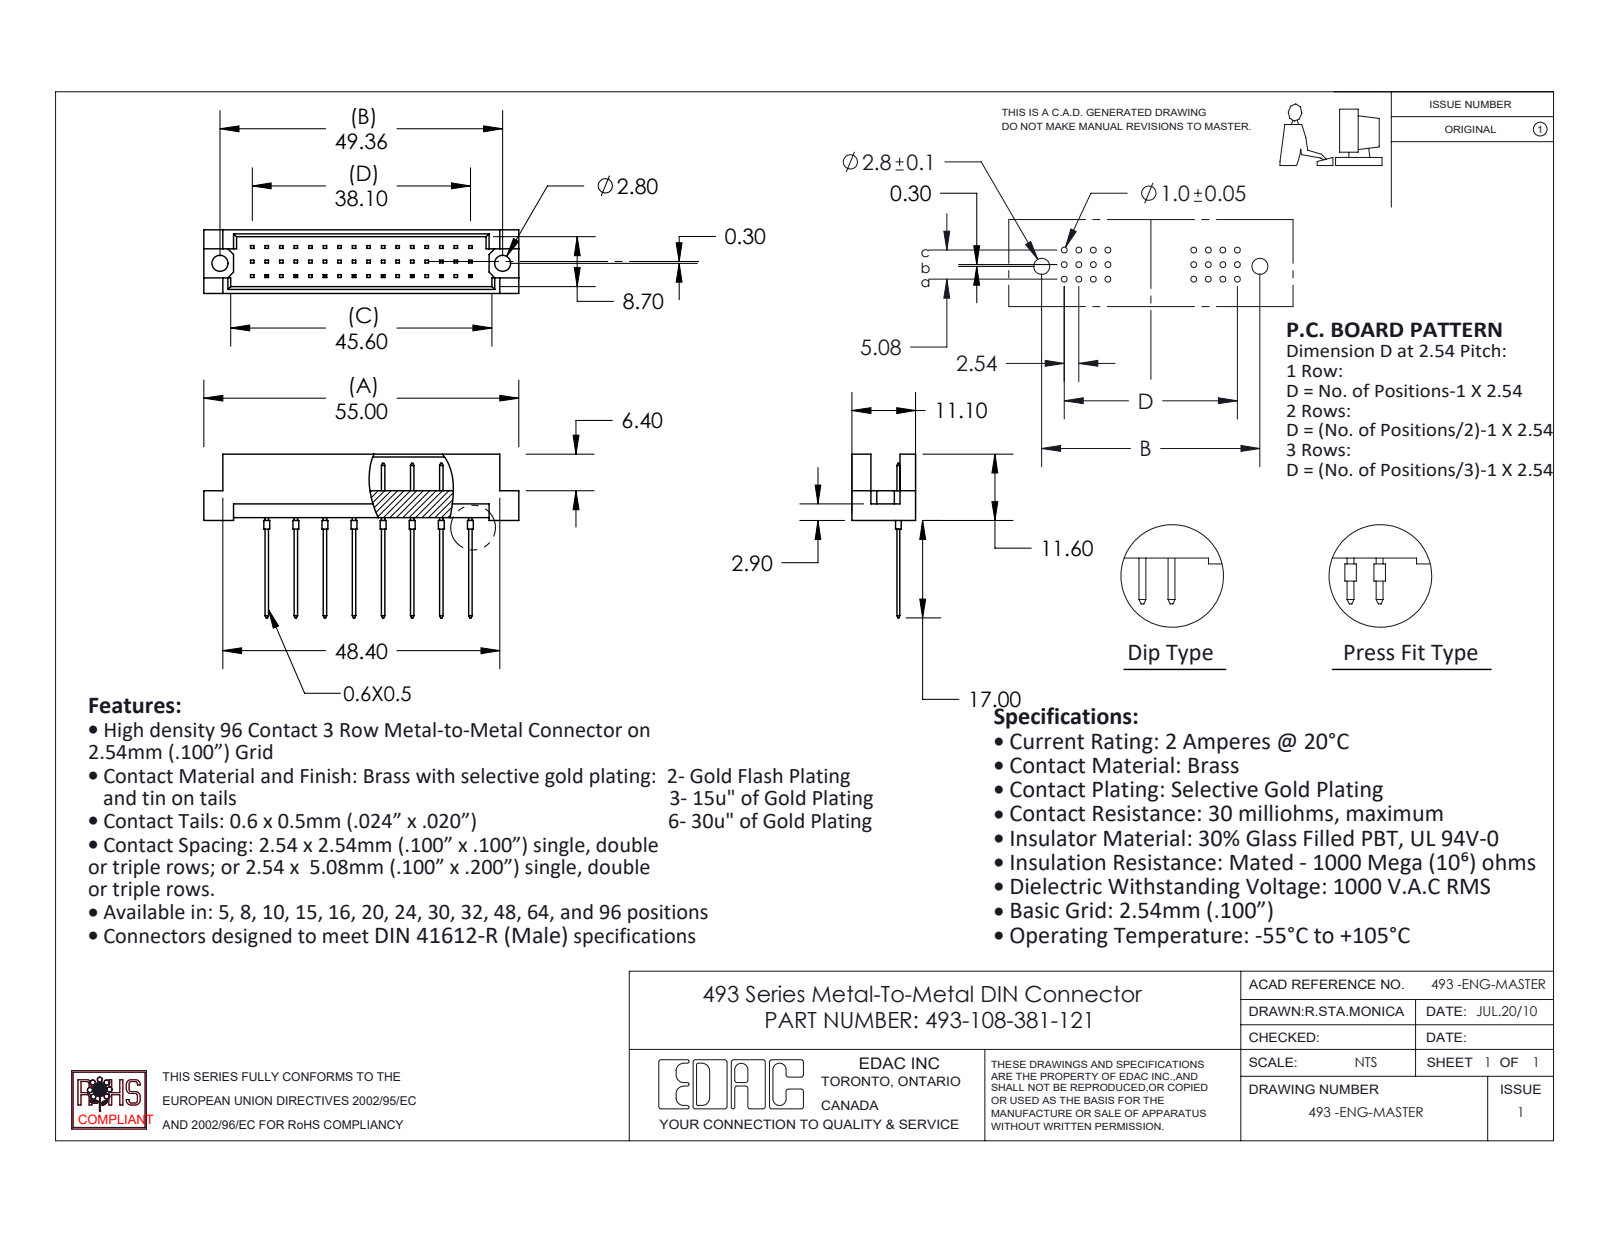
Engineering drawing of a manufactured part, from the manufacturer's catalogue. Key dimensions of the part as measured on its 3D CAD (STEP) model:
Part name (STEP PRODUCT): 493-108-381-121; 493-290_81; 493 Part_48
STEP written by: SolidWorks 2020 (CONFIG_CONTROL_DESIGN)
Units: millimetres
Bodies: 9 solids, 420 faces (400 planar, 20 cylindrical, 0 other)
Overall size (bounding box): 55 × 28.6 × 11.1
Volume: 3 342 mm³ · Surface area: 4 248 mm²
Round holes (diameter × count): ⌀2.8 ×2
Round bosses / shafts (diameter × count): ⌀1 ×8
Main face-to-face distances: 1.2, 9.9, 11.1, 8.7, 5.08, 4.7, 0.5, 10.16, 2.76, 8.34
Hole centre spacings: 49.36
